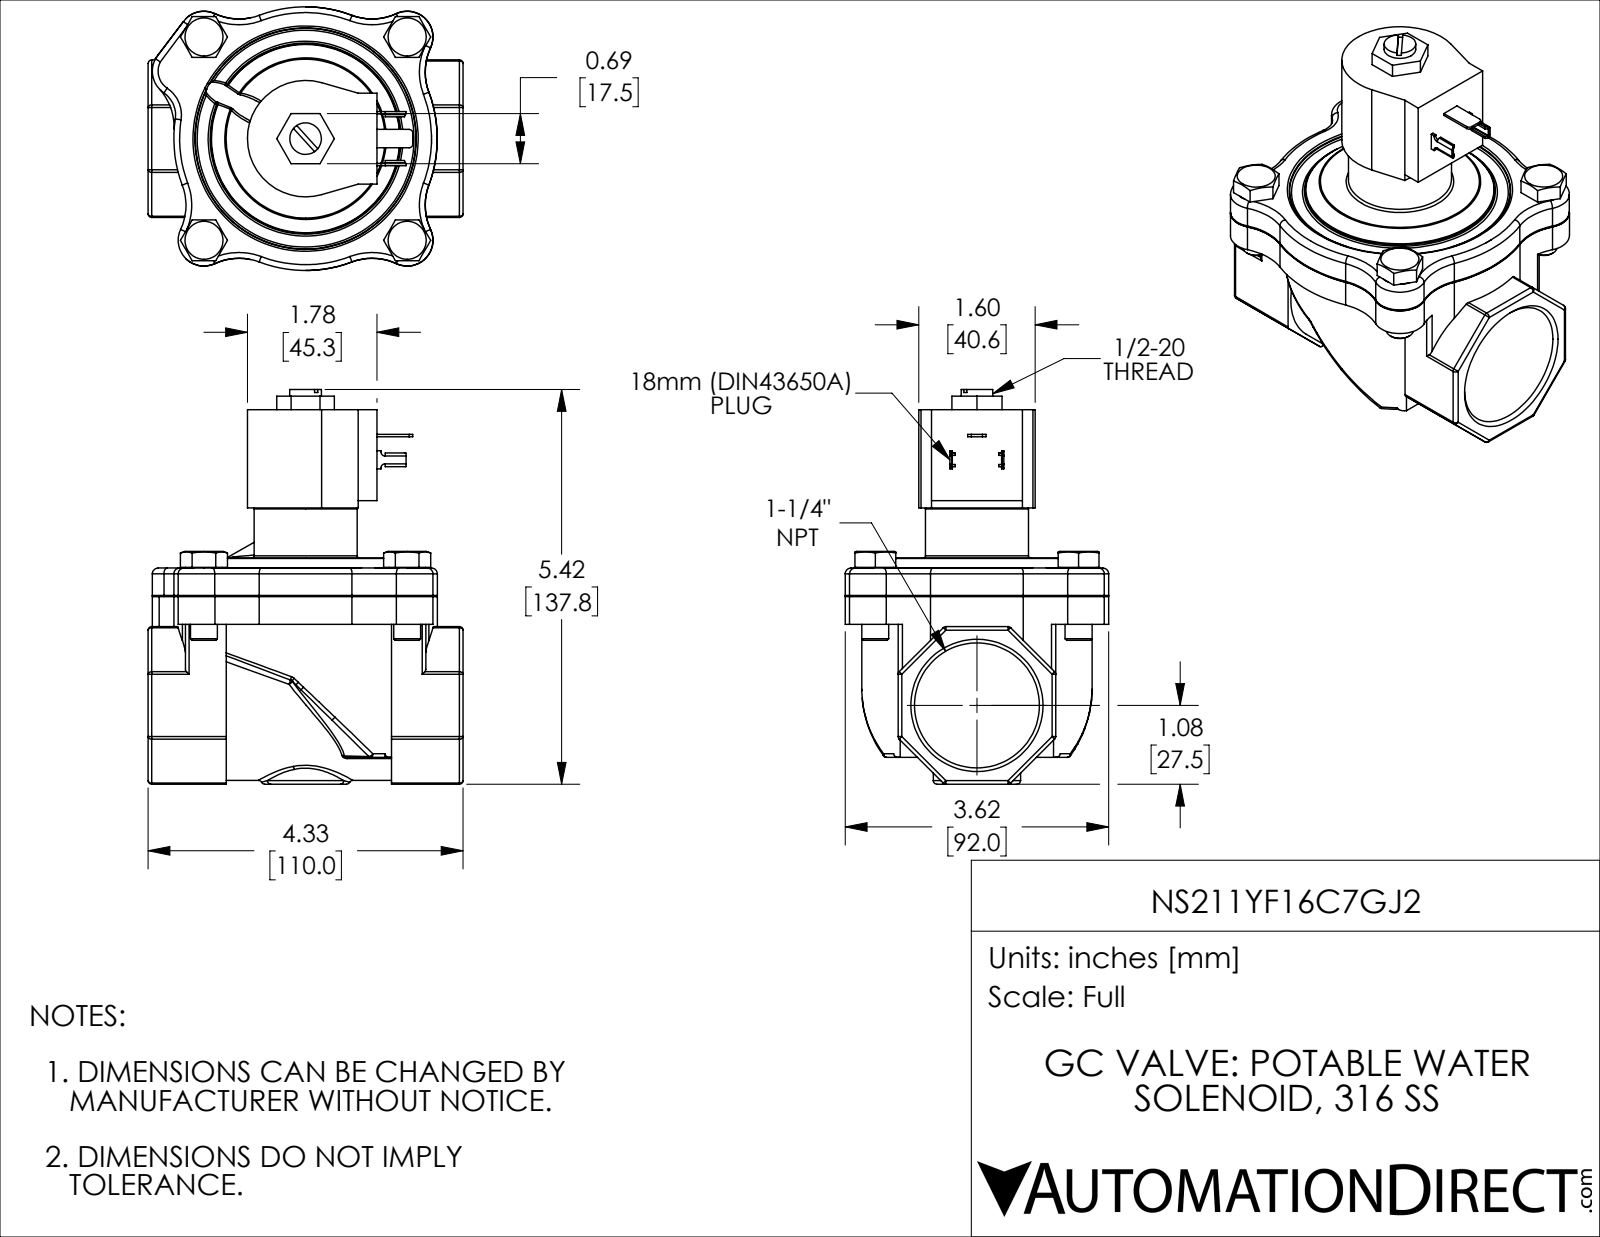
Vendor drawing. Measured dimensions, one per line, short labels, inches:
name: NS211YF16C7GJ2
written by: SolidWorks 2018 (AUTOMOTIVE_DESIGN)
unit: in
bodies: 9 solids, 503 faces (155 planar, 161 cylindrical, 187 other)
size: 5.424 × 4.33 × 3.622
volume: 26.48 in³; area: 135.5 in²
holes: 4× ⌀0.375, 4× ⌀0.433, 1× ⌀0.125, 1× ⌀0.434, 1× ⌀0.846, 1× ⌀0.949, 1× ⌀1.718
bosses: 4× ⌀0.504, 4× ⌀0.37, 1× ⌀1.417
rounds: 32× R0.05, 15× R0.787, 8× R0.354, 4× R0.006, 4× R0.041, 2× R0.06, 2× R0.362, 2× R1.811
face distances: 0.393, 1.22, 0.827, 2.57, 2.177, 1.35, 2.578, 2.97, 3.798, 5.148
hole spacings: 2.795, 1.976, 1.977, 2.794, 2.795, 3.952, 3.953
